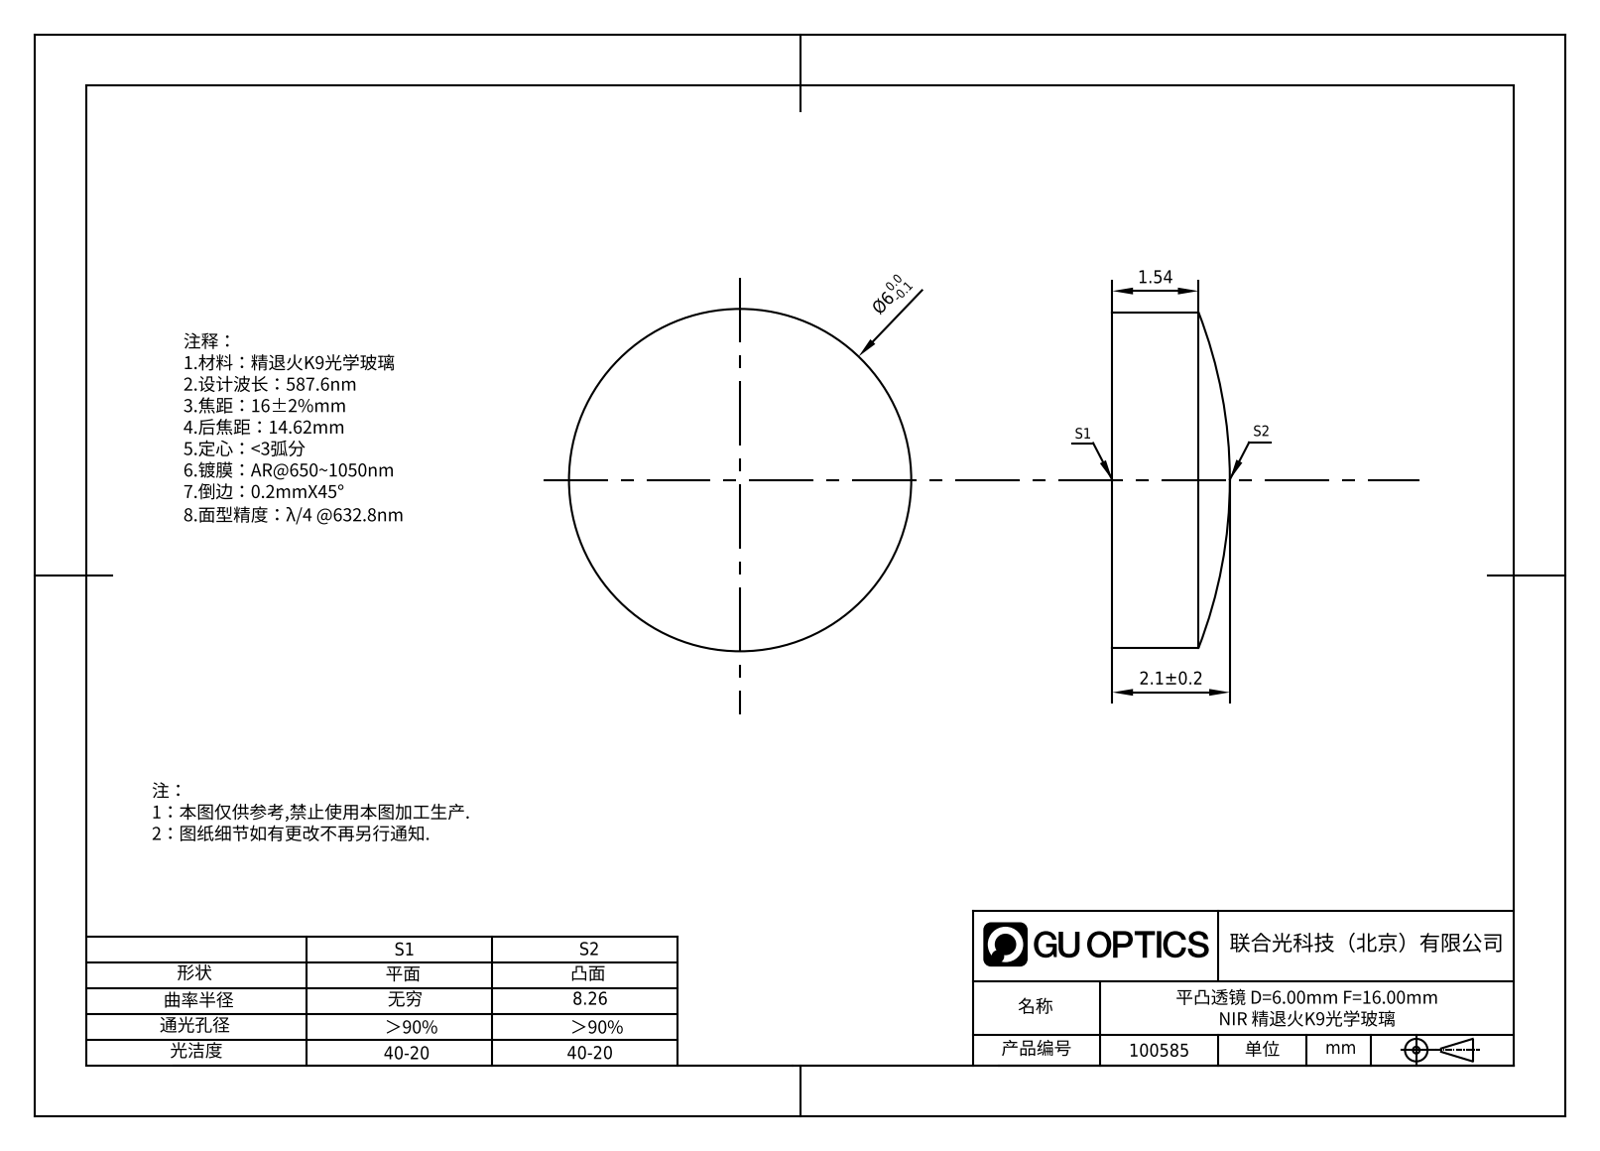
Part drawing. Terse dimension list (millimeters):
name: 100585
written by: SolidWorks 2020 (CONFIG_CONTROL_DESIGN)
unit: mm
bodies: 1 solid, 5 faces (1 planar, 2 cylindrical, 2 other)
size: 6 × 6 × 2.1
volume: 52 mm³; area: 87 mm²
bosses: 1× ⌀6
